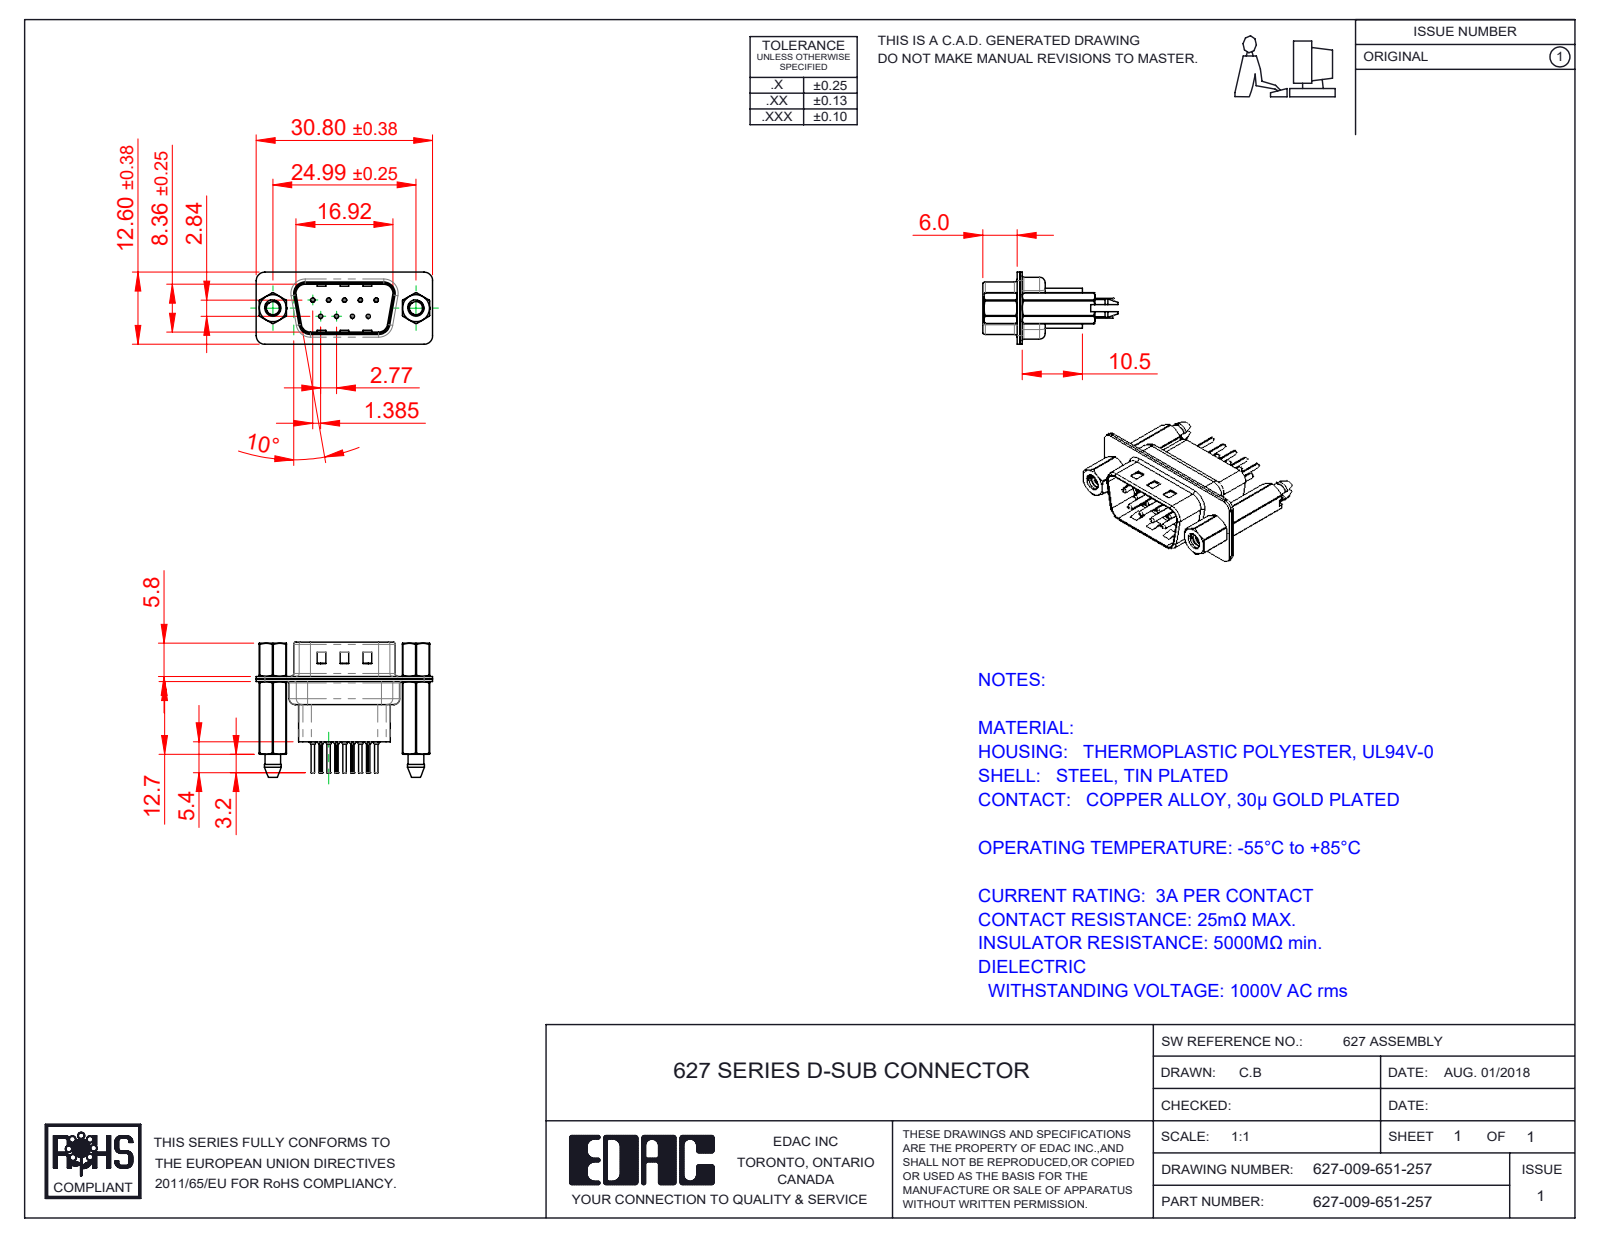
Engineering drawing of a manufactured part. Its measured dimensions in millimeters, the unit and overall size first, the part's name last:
Units: millimetres
Overall size (bounding box): 30.8 × 23.6 × 12.6
Round holes (diameter × count): ⌀0.2 ×9, ⌀0.35 ×9, ⌀1.1 ×9, ⌀1.6 ×9, ⌀2.26 ×2, ⌀2.29 ×2, ⌀4 ×2, ⌀4.8 ×2
Round bosses / shafts (diameter × count): ⌀2 ×9, ⌀1.5 ×9, ⌀0.75 ×9, ⌀0.6 ×9, ⌀4.9 ×2, ⌀2.79 ×2
Partial cylindrical surfaces — rounded edges, fillets, slot ends (radius × count): R1.5 ×20, R0.1 ×18, R2 ×12, R1.6 ×10, R0.5 ×8, R0.25 ×4, R0.6 ×4, R0.65 ×4
Main face-to-face distances: 0.45, 0.4, 0.9, 4.76, 0.82, 9.58, 1.4, 1.5, 0.68, 7.68
Hole centre spacings: 3.16, 2.77, 5.54, 5.03, 5.04, 8.31, 7.48, 7.49
Volume: 2 299 mm³ · Surface area: 5 905 mm²
Bodies: 16 solids, 1420 faces (377 planar, 600 cylindrical, 443 other)
Part name (STEP PRODUCT): 627 Contact Row 2_41; 627 Housing_09 HP; 627 Shell Rear_09 Contacts; 627 4-40 Threaded Boardlock_HP51 (+4 more)
STEP written by: SolidWorks 2020 (CONFIG_CONTROL_DESIGN)
